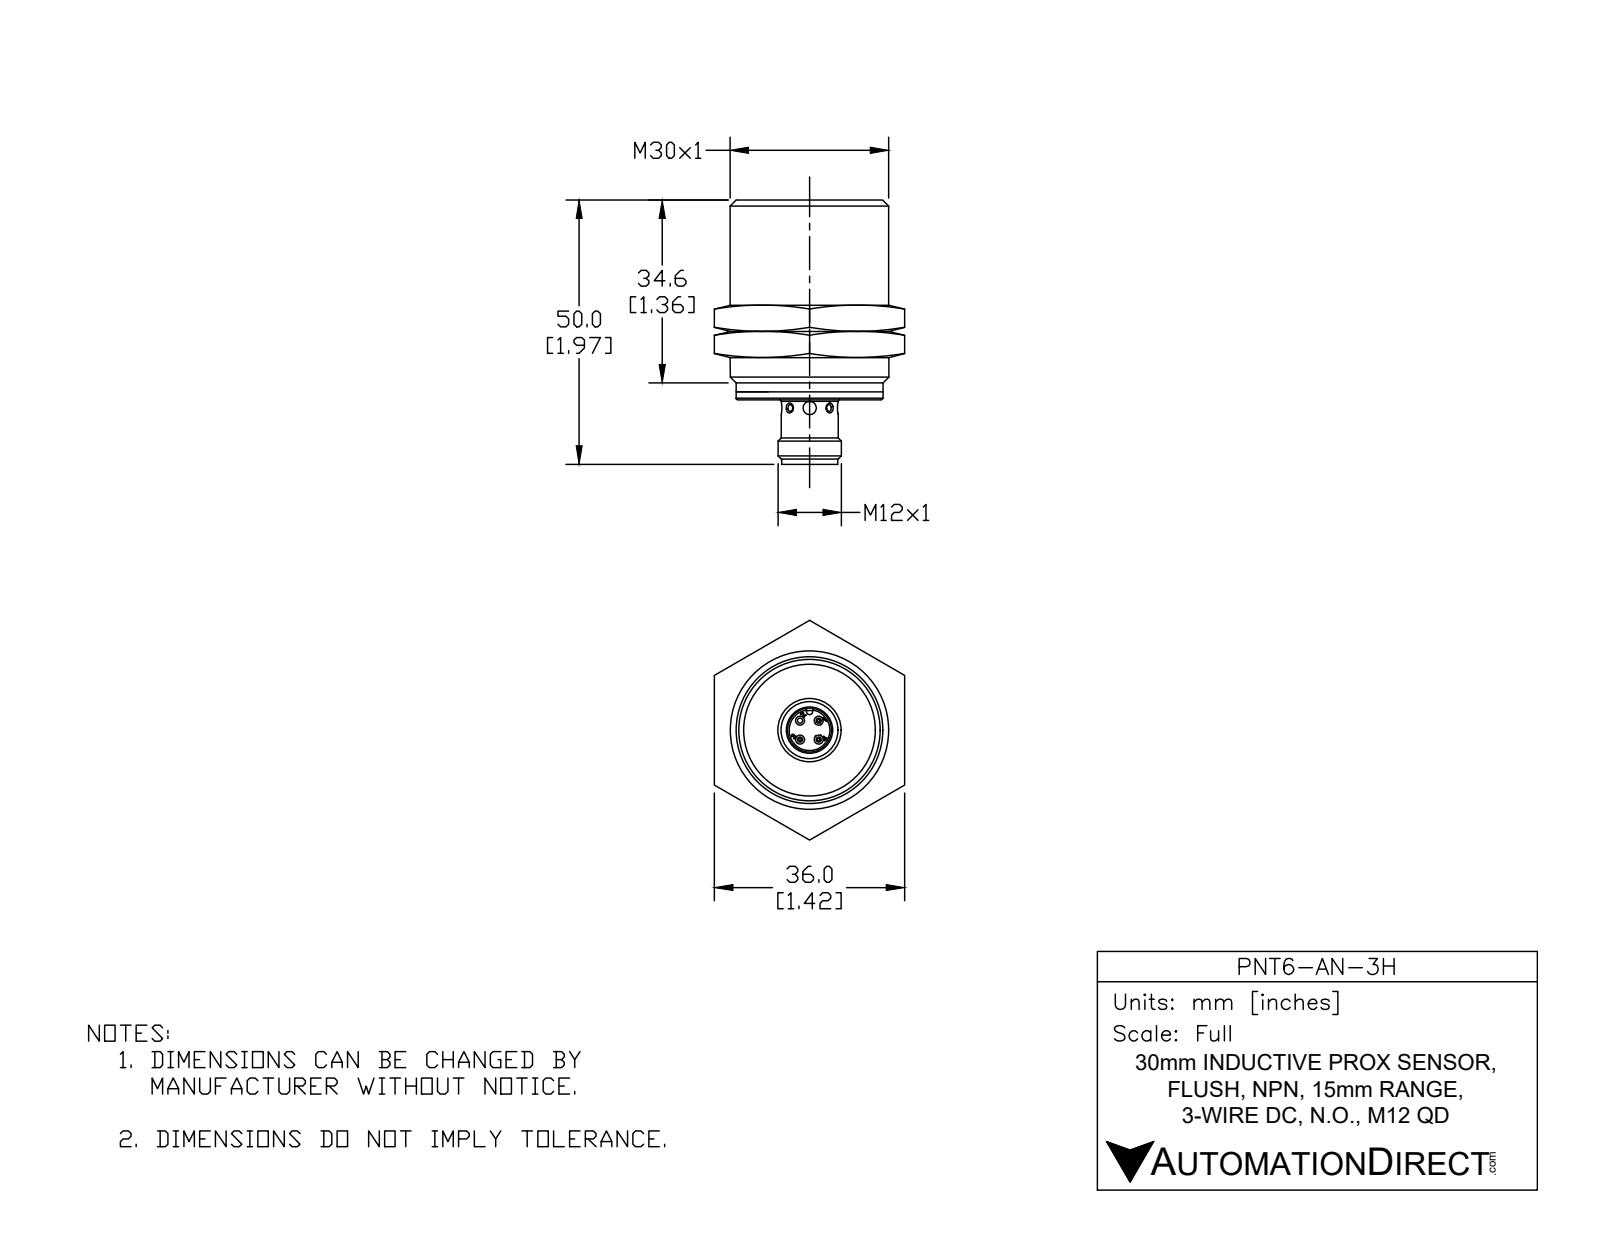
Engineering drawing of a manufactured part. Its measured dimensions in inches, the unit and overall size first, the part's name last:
Units: inches
Overall size (bounding box): 1.969 × 1.181 × 1.181
Round holes (diameter × count): ⌀0.043 ×3, ⌀0.04 ×2, ⌀0.098 ×2, ⌀0.038 ×1, ⌀0.04 ×1, ⌀0.323 ×1, ⌀0.327 ×1, ⌀0.394 ×1, ⌀1.047 ×1, ⌀1.076 ×1, ⌀1.089 ×1
Round bosses / shafts (diameter × count): ⌀0.039 ×9, ⌀1.181 ×1, ⌀1.094 ×1, ⌀1.083 ×1, ⌀1.074 ×1, ⌀1.044 ×1, ⌀0.878 ×1, ⌀0.472 ×1
Partial cylindrical surfaces — rounded edges, fillets, slot ends (radius × count): R0.004 ×12, R0.02 ×8, R0.03 ×3, R0.039 ×3, R0.024 ×1, R0.031 ×1
Main face-to-face distances: 0.126, 1.488, 1.362, 0.037, 0.089, 1.451, 0.098, 1.461, 0.028, 0.024
Hole centre spacings: 0.098, 0.139, 0.197
Volume: 1.573 in³ · Surface area: 12.79 in²
Bodies: 1 solid, 515 faces (161 planar, 130 cylindrical, 224 other)
Part name (STEP PRODUCT): PNT6-AN-3H
STEP written by: SolidWorks 2017 (AUTOMOTIVE_DESIGN)
